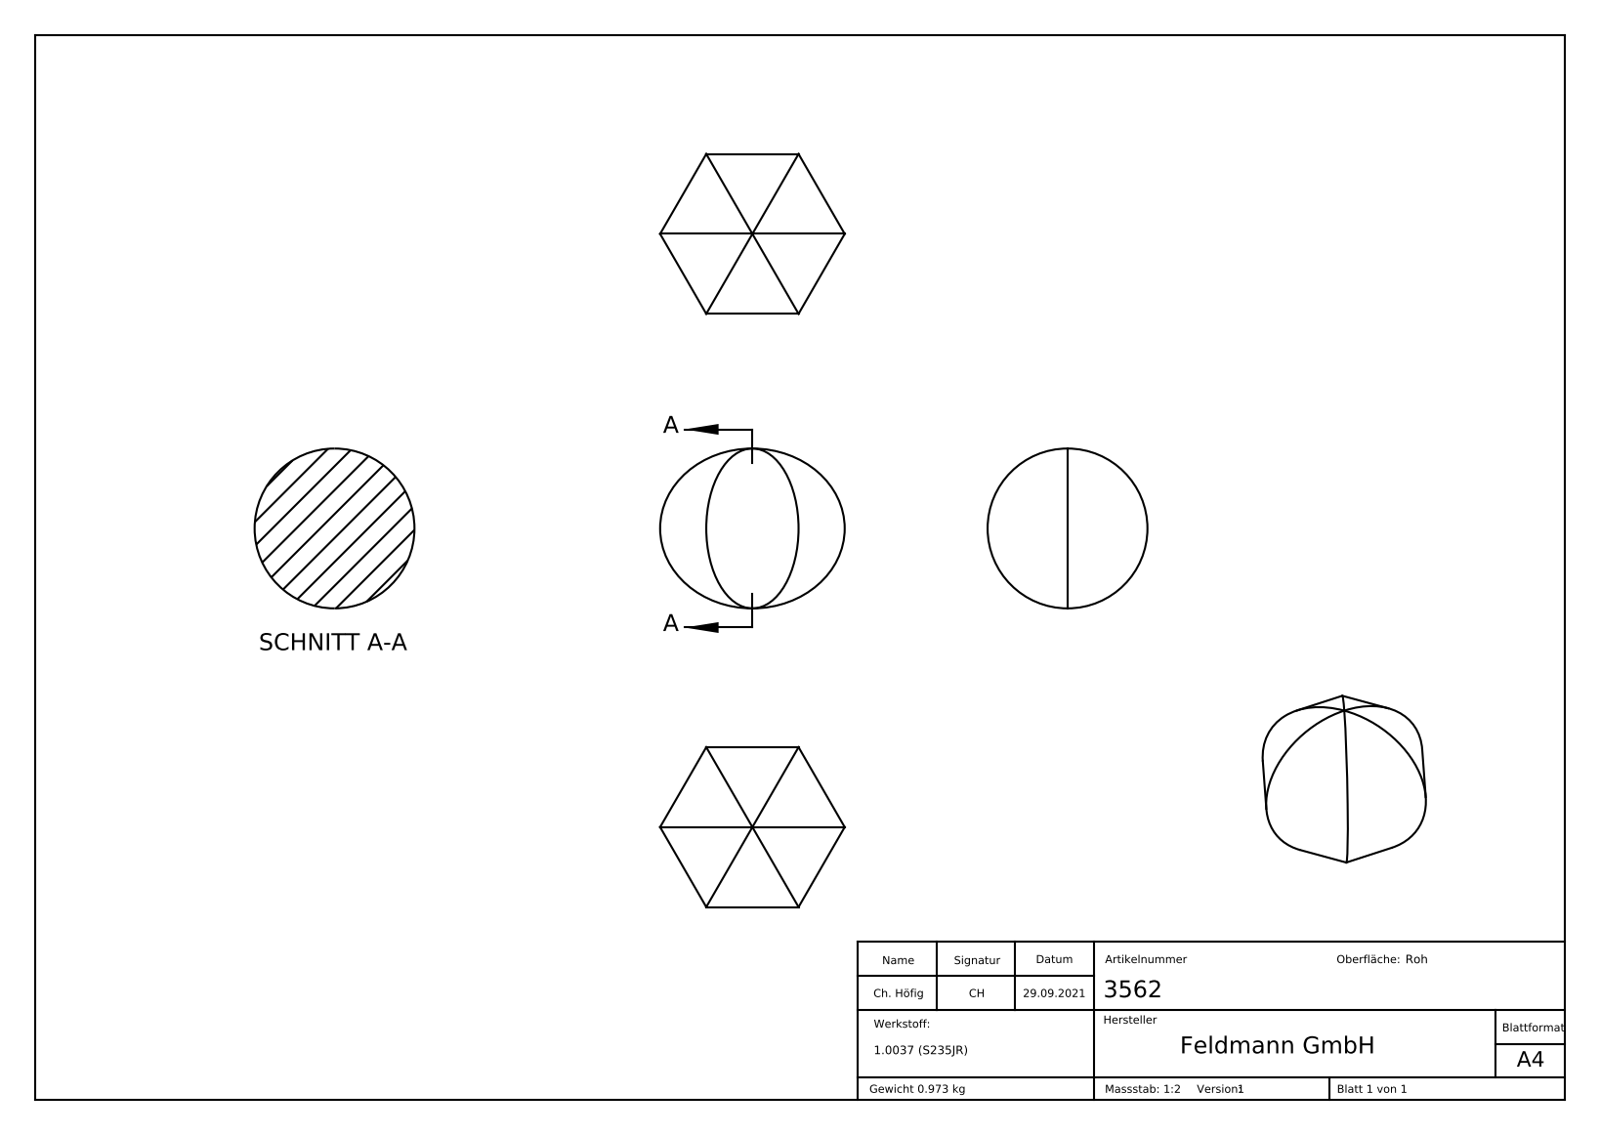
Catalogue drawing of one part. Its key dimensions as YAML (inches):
part_name: "3562"
step_written_by: "SolidWorks 2018 (CONFIG_CONTROL_DESIGN)"
units: inches
bodies: {solids: 1, faces: 6, planar: 0, cylindrical: 6, other: 0}
overall_size: [2.728, 2.362, 2.362]
volume: 7.61
surface_area: 19.33
round_bosses_or_shafts:
  - {diameter: 2.362, count: 3}
